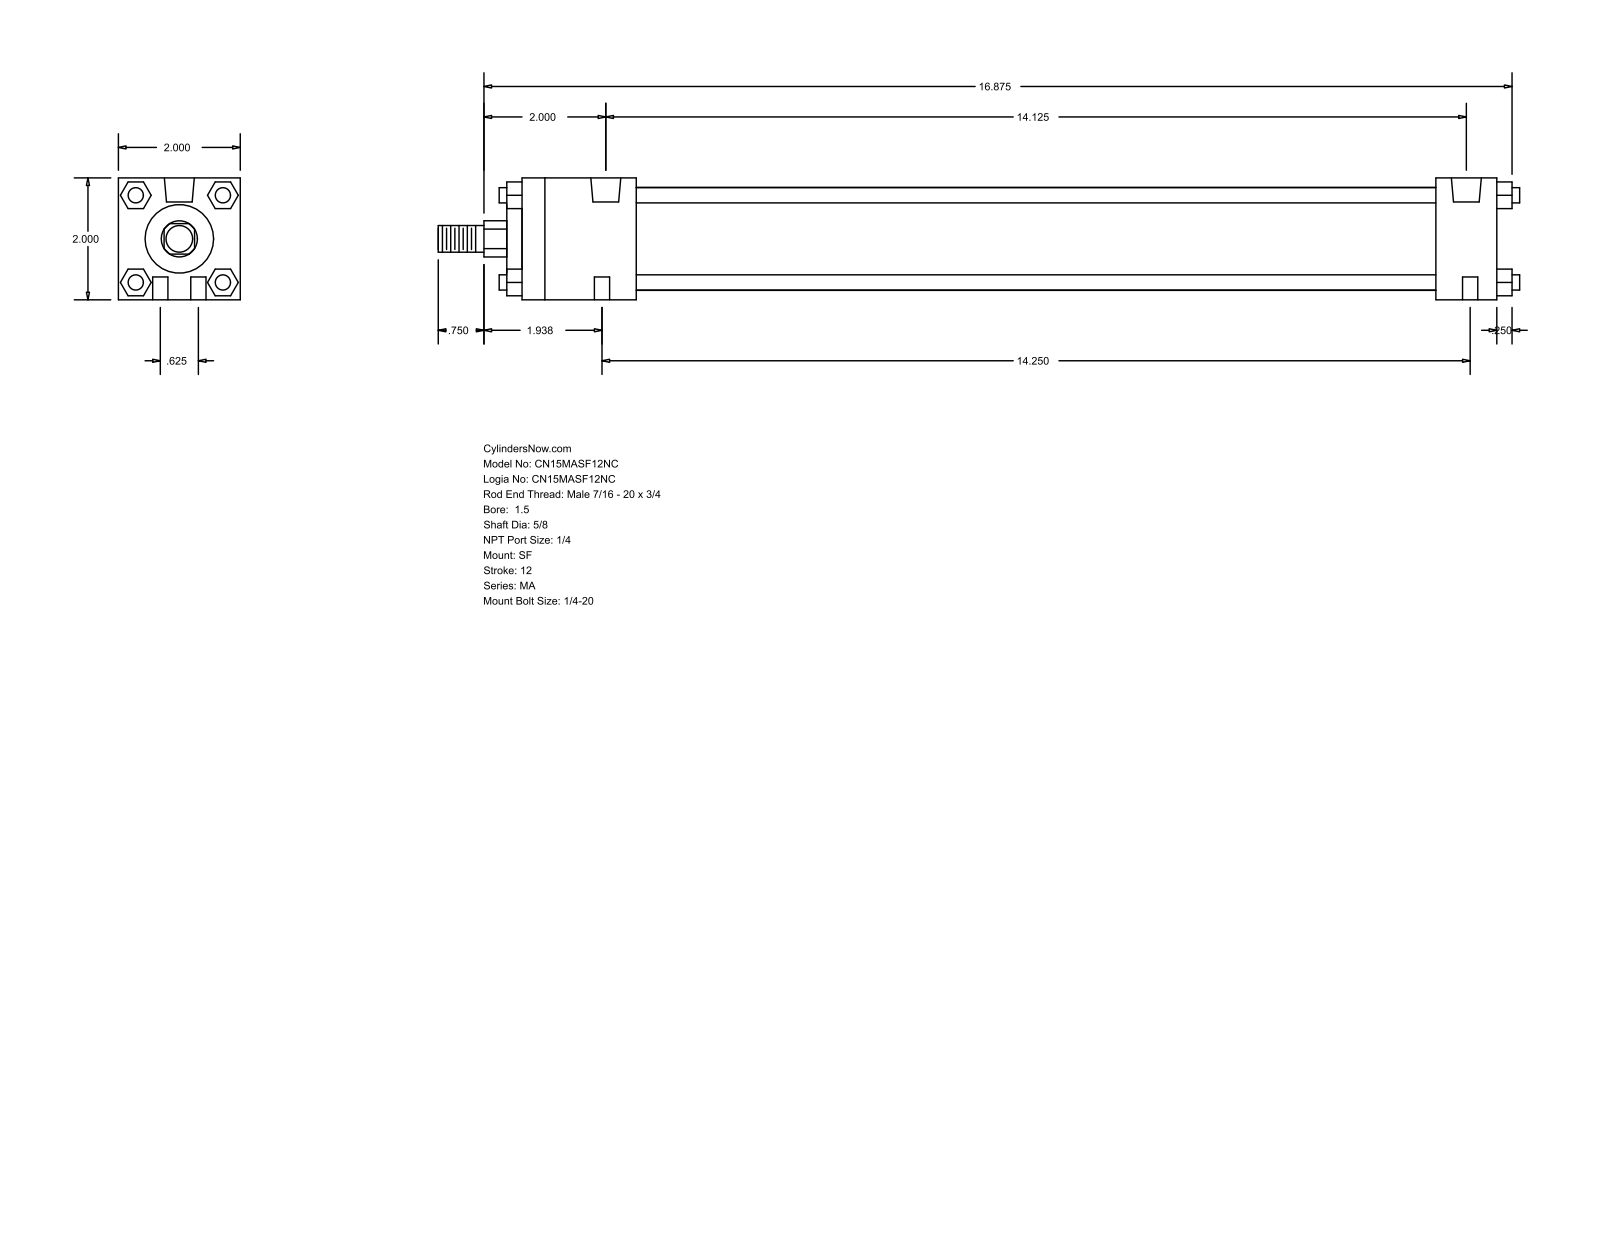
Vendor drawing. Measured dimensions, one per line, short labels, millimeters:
name: MA_SF__0150_0.625
written by: GSSL Pune (CONFIG_CONTROL_DESIGN)
unit: mm
bodies: 0 solids, 124 faces (94 planar, 30 cylindrical, 0 other)
size: 450.85 × 50.8 × 50.8
holes: 4× ⌀6.35, 2× ⌀7.94, 2× ⌀12.49
bosses: 4× ⌀6.35, 1× ⌀42.93, 1× ⌀28.57, 1× ⌀15.88, 1× ⌀11.11
rounds: 1× R7.54
face distances: 50.8, 406.39, 6.35, 412.74, 47.62, 381, 333.38, 358.77, 25.39, 53.97
hole spacings: 8.1, 360.45, 15.88, 358.77, 361.95, 362.3
